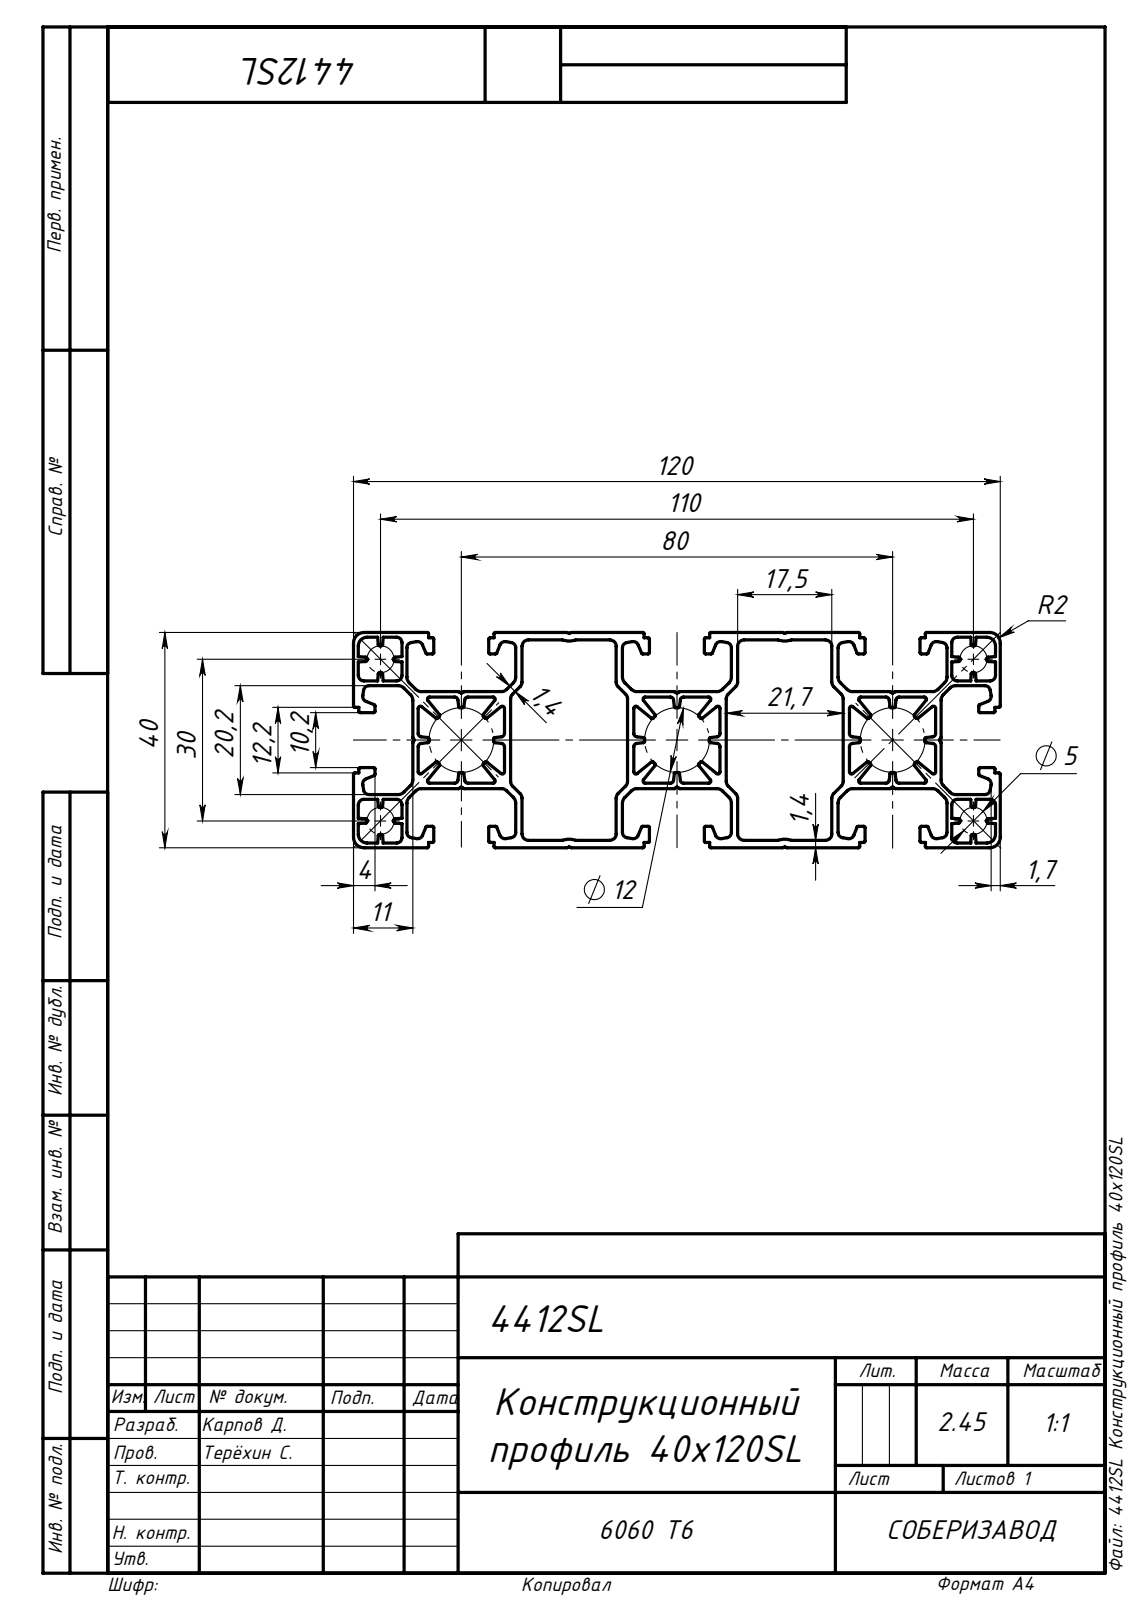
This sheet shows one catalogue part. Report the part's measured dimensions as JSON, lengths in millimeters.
{"step_written_by": "SolidWorks 2019 (AUTOMOTIVE_DESIGN)", "units": "millimeters", "bodies": {"solids": 1, "faces": 758, "planar": 390, "cylindrical": 368, "other": 0}, "overall_size": [1000, 120, 40], "volume_mm3": 909081, "surface_area_mm2": 1358000, "partial_cylinders_radius": [[0.25, 160], [1, 44], [1.5, 32], [0.4, 24], [0.6, 24], [1.2, 24], [1.6, 4], [2, 4]], "face_to_face_distances": [40, 11, 29, 2.1, 1.4, 1, 28, 30.1, 0.9, 9]}
